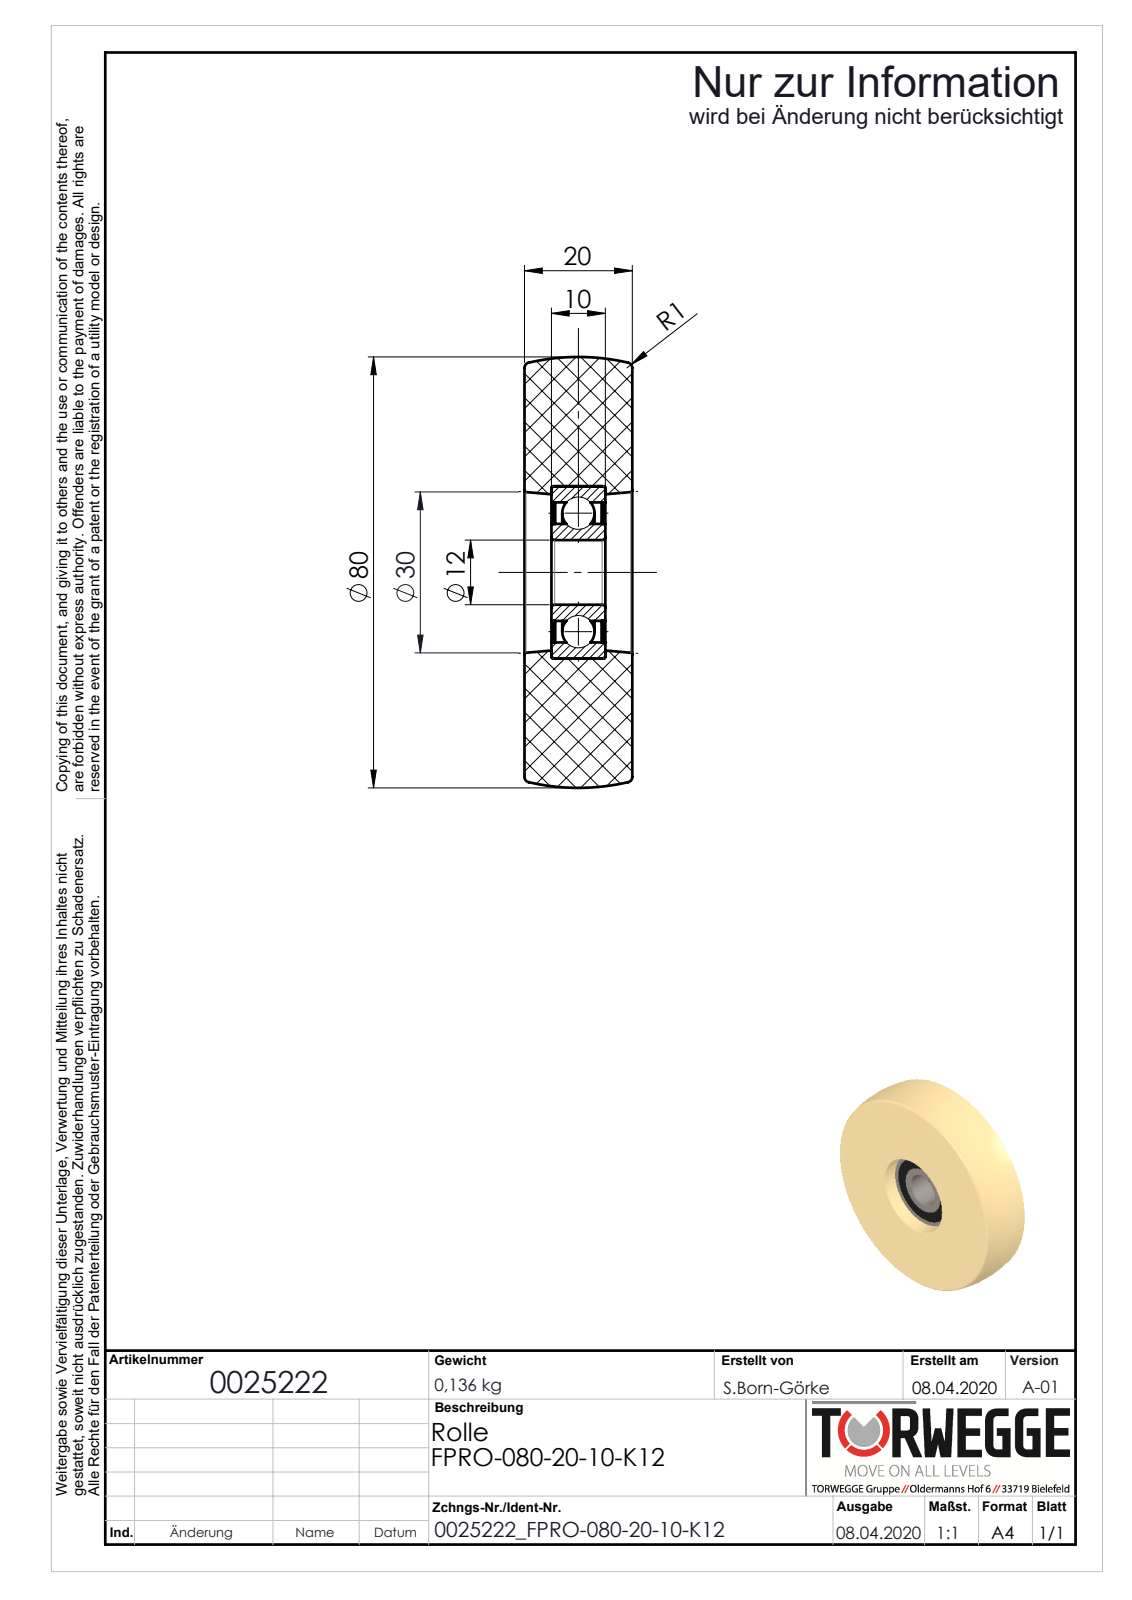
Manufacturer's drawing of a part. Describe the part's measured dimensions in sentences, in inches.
The part is named "0025222". Its 3-D file was written by "SolidWorks 2018 (AUTOMOTIVE_DESIGN)". It is 4 solids with 64 faces: 12 planar, 22 cylindrical and 30 other. Overall it measures 3.15 by 3.066 by 0.787 inches. Its volume is 5.461 cubic inches and its surface area 30.8 square inches. Round holes: 1 of diameter 0.472, 1 of diameter 0.709, 1 of diameter 1.024, 1 of diameter 1.26. The main face-to-face distances are 0.787, 0.197, 0.591, 0.205, 0.224, 0.563, 0.583, 0.028, 0.366, 0.386.
